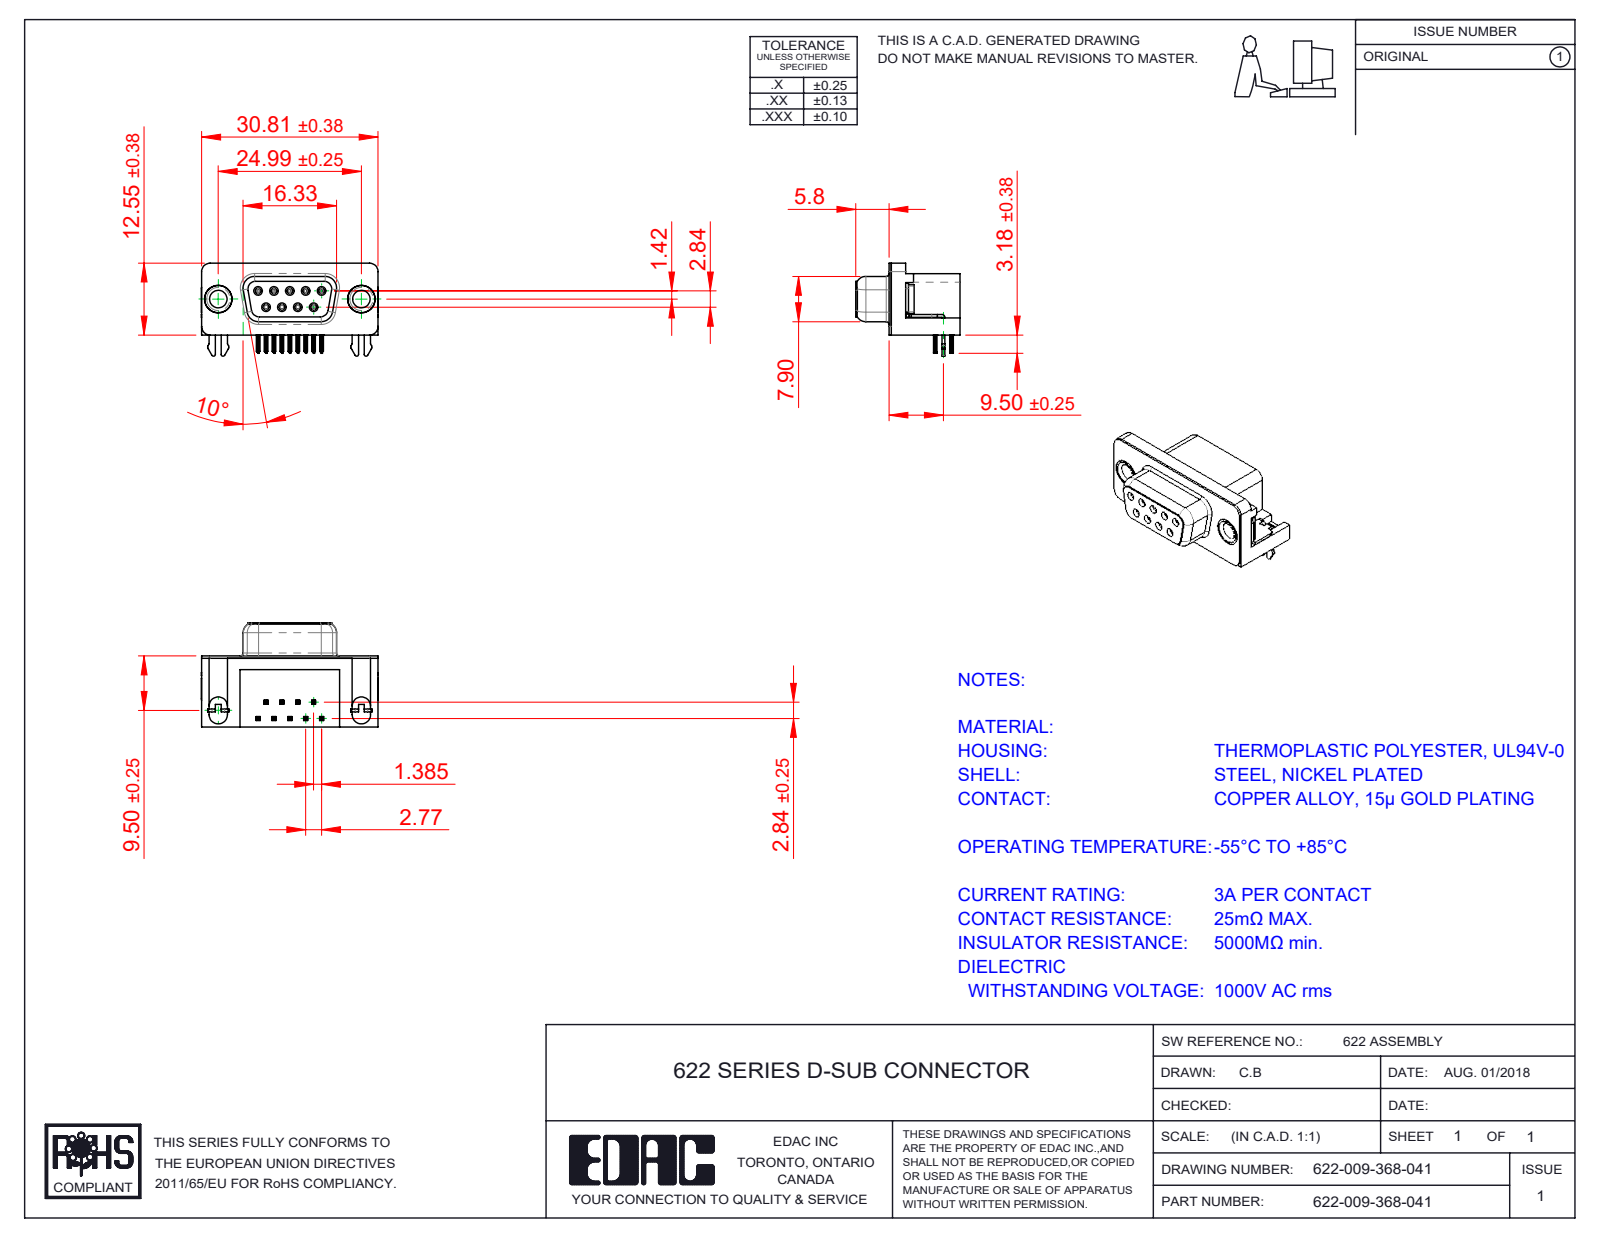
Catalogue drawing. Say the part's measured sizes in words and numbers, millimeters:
The part is named "622 4 Prong Board Lock; 622 Contact Top; 622 Housing_9 Socket; 622-009-368-041 (+3 more)". Its 3-D file was written by "SolidWorks 2016 (CONFIG_CONTROL_DESIGN)". It is 15 solids with 1652 faces: 726 planar, 404 cylindrical and 522 other. Overall it measures 30.89 by 18.2 by 16.25 millimeters. Its volume is 3 723 cubic millimeters and its surface area 5 125 square millimeters. Round holes: 9 of diameter 0.8, 9 of diameter 0.9, 2 of diameter 2, 2 of diameter 3.05, 2 of diameter 4, 2 of diameter 4.8, 2 of diameter 5. Round bosses or shafts: 9 of diameter 1.2, 2 of diameter 4.9, 2 of diameter 4.75, 2 of diameter 3.85, 2 of diameter 3. Partial cylindrical surfaces (rounded edges, fillets, slot ends): 72 of radius 0.1, 36 of radius 0.15, 18 of radius 0.35, 18 of radius 1, 12 of radius 0.25, 9 of radius 0.34, 8 of radius 1.35, 8 of radius 1.6. The main face-to-face distances are 0.4, 12, 12.4, 0.35, 2.9, 2.5, 6.2, 10.34, 9.5, 5.8. The hole center spacings are 3.16, 2.77, 5.54, 5.03, 5.04, 8.31, 7.48, 7.49.
